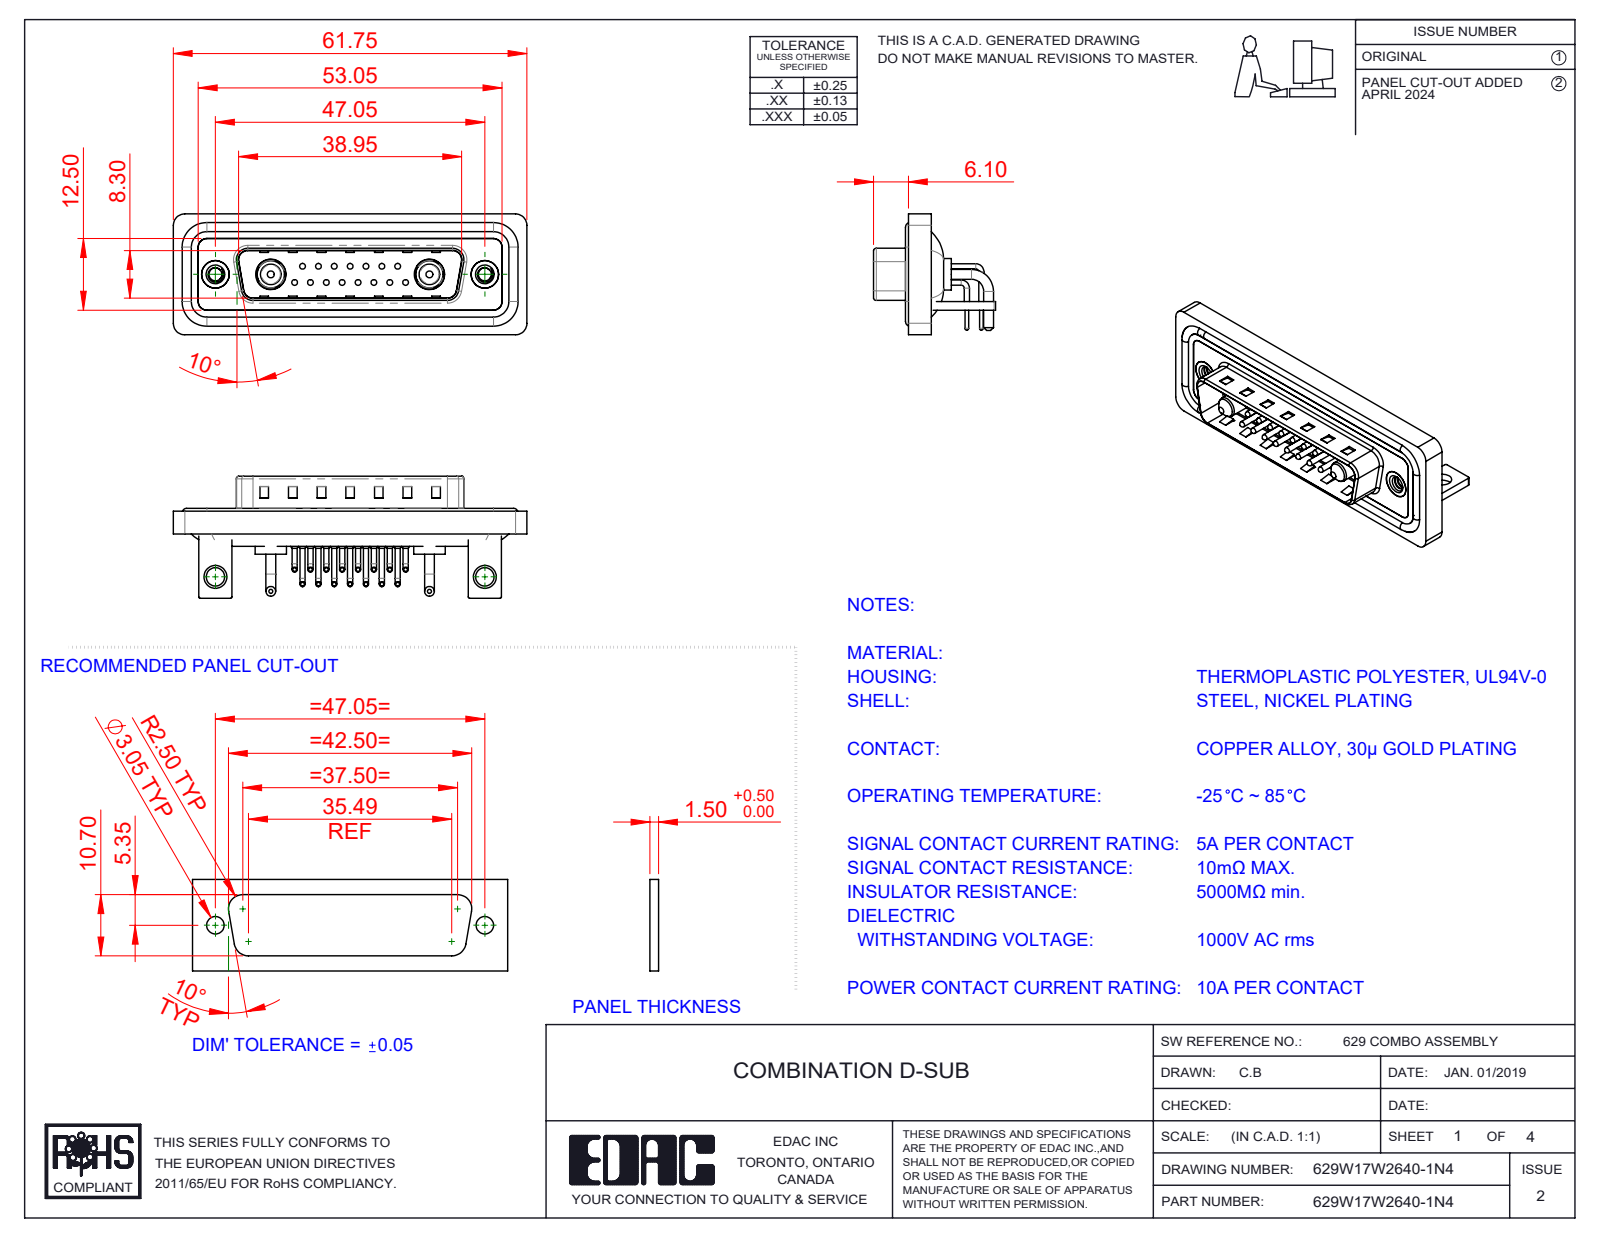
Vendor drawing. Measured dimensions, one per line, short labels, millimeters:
name: 629Combo Threaded Rivet_3; 629Combo Shell Front_25 Contacts; 629Combo Contact Row 1; 629W17W2640-1N4 (+6 more)
written by: SolidWorks 2023 (CONFIG_CONTROL_DESIGN)
unit: mm
bodies: 28 solids, 2259 faces (1209 planar, 788 cylindrical, 262 other)
size: 61.75 × 21.3 × 21.1
volume: 7 674 mm³; area: 13 086 mm²
holes: 15× ⌀0.75, 15× ⌀1.6, 15× ⌀2, 2× ⌀2.26, 2× ⌀3.2, 2× ⌀4, 2× ⌀4.8, 2× ⌀4.85, 2× ⌀5, 2× ⌀5.3
bosses: 30× ⌀0.9, 15× ⌀1.5, 15× ⌀1, 15× ⌀0.65, 4× ⌀1.7, 4× ⌀1.6, 2× ⌀5.5, 2× ⌀5.2
rounds: 19× R2, 18× R1.5, 16× R0.25, 15× R1.01, 9× R0.5, 8× R1.6, 4× R0.6, 4× R0.65
face distances: 0.4, 0.8, 1.5, 2.1, 2.9, 1.1, 4.1, 1.6, 4.5, 3.7
hole spacings: 3.16, 2.77, 5.54, 8.31, 5.04, 7.49, 11.08, 5.03
